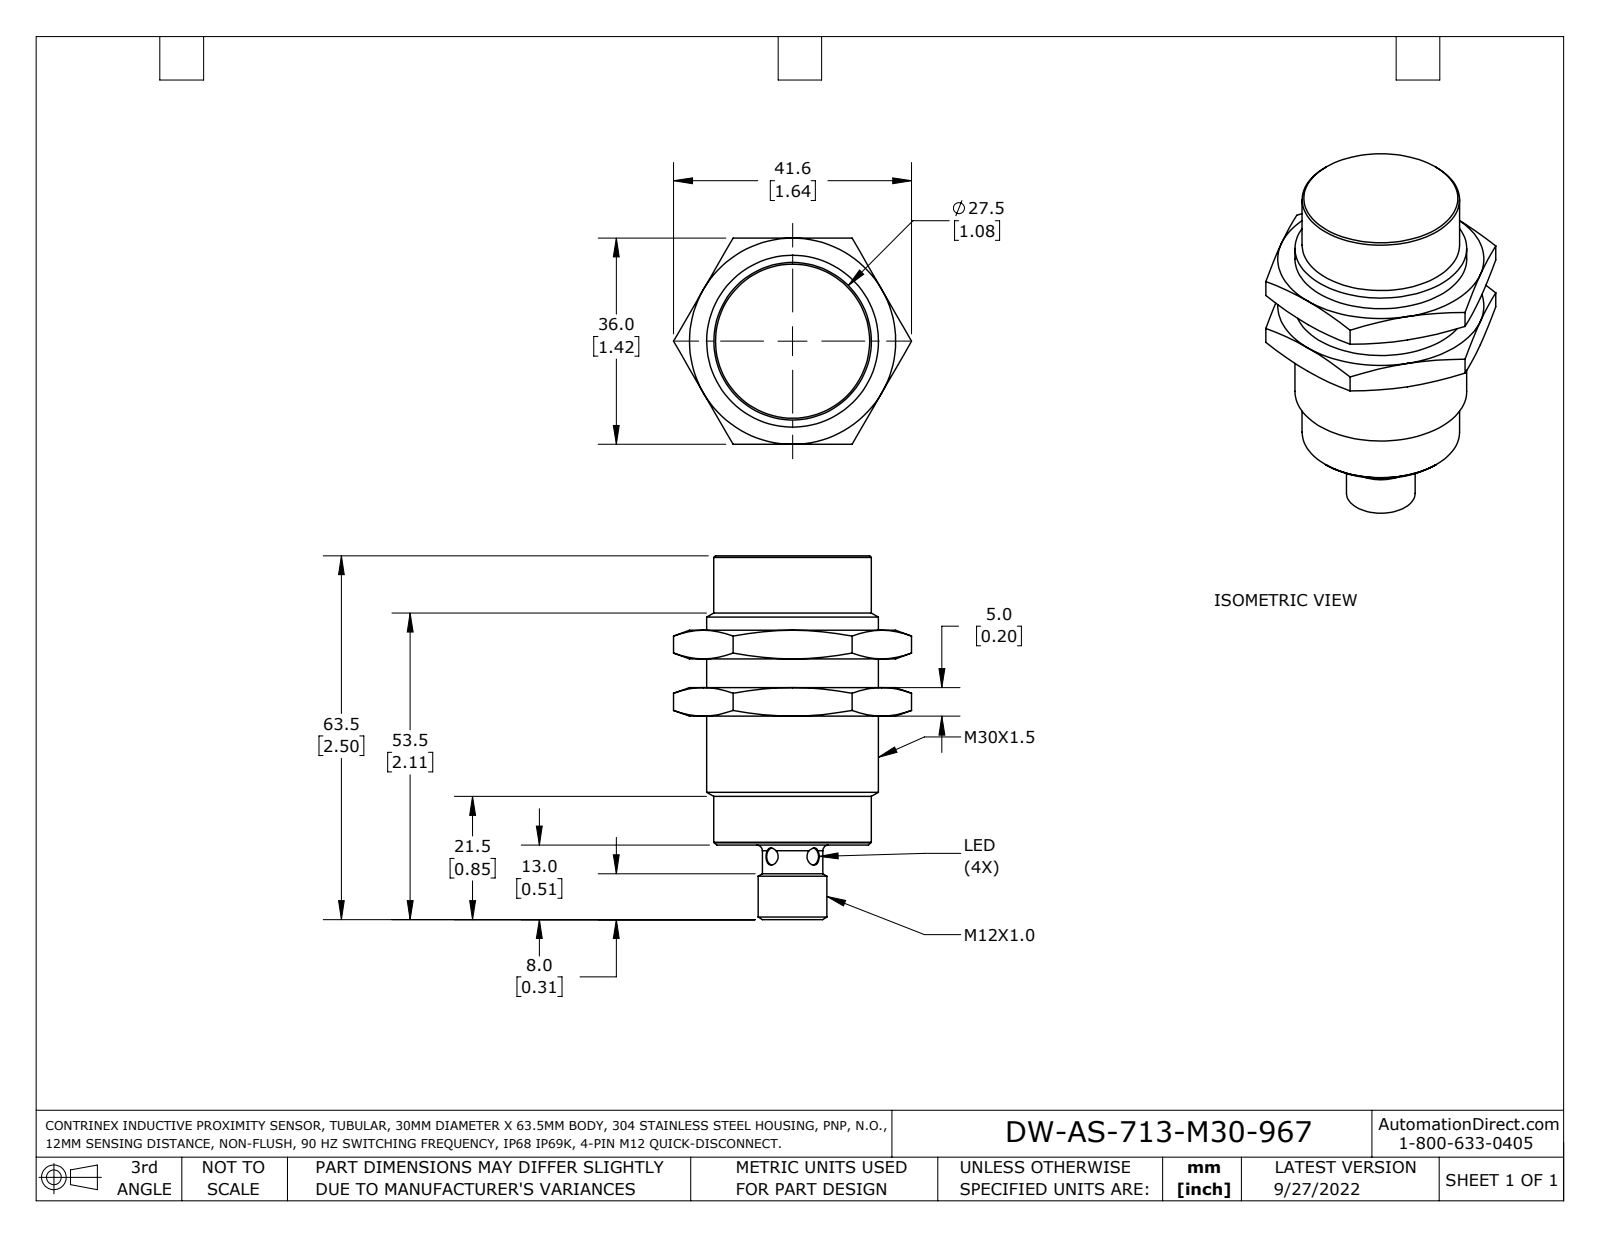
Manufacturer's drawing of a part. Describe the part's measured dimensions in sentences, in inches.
The part is named "DW-AS-713-M30-967". Its 3-D file was written by "SolidWorks 2021 (AUTOMOTIVE_DESIGN)". It is 1 solid with 83 faces: 27 planar, 19 cylindrical and 37 other. Overall it measures 2.5 by 1.637 by 1.417 inches. Its volume is 2.343 cubic inches and its surface area 13.21 square inches. Round holes: 2 of diameter 0.118, 1 of diameter 0.335. Round bosses or shafts: 4 of diameter 0.039, 1 of diameter 1.181, 1 of diameter 1.083, 1 of diameter 1.075, 1 of diameter 0.472, 1 of diameter 0.415. Partial cylindrical surfaces (rounded edges, fillets, slot ends): 2 of radius 0.022. The main face-to-face distances are 0.197, 0.394, 1.417, 1.988, 0.512, 0.709, 1.102, 1.28, 0.886, 0.591.
